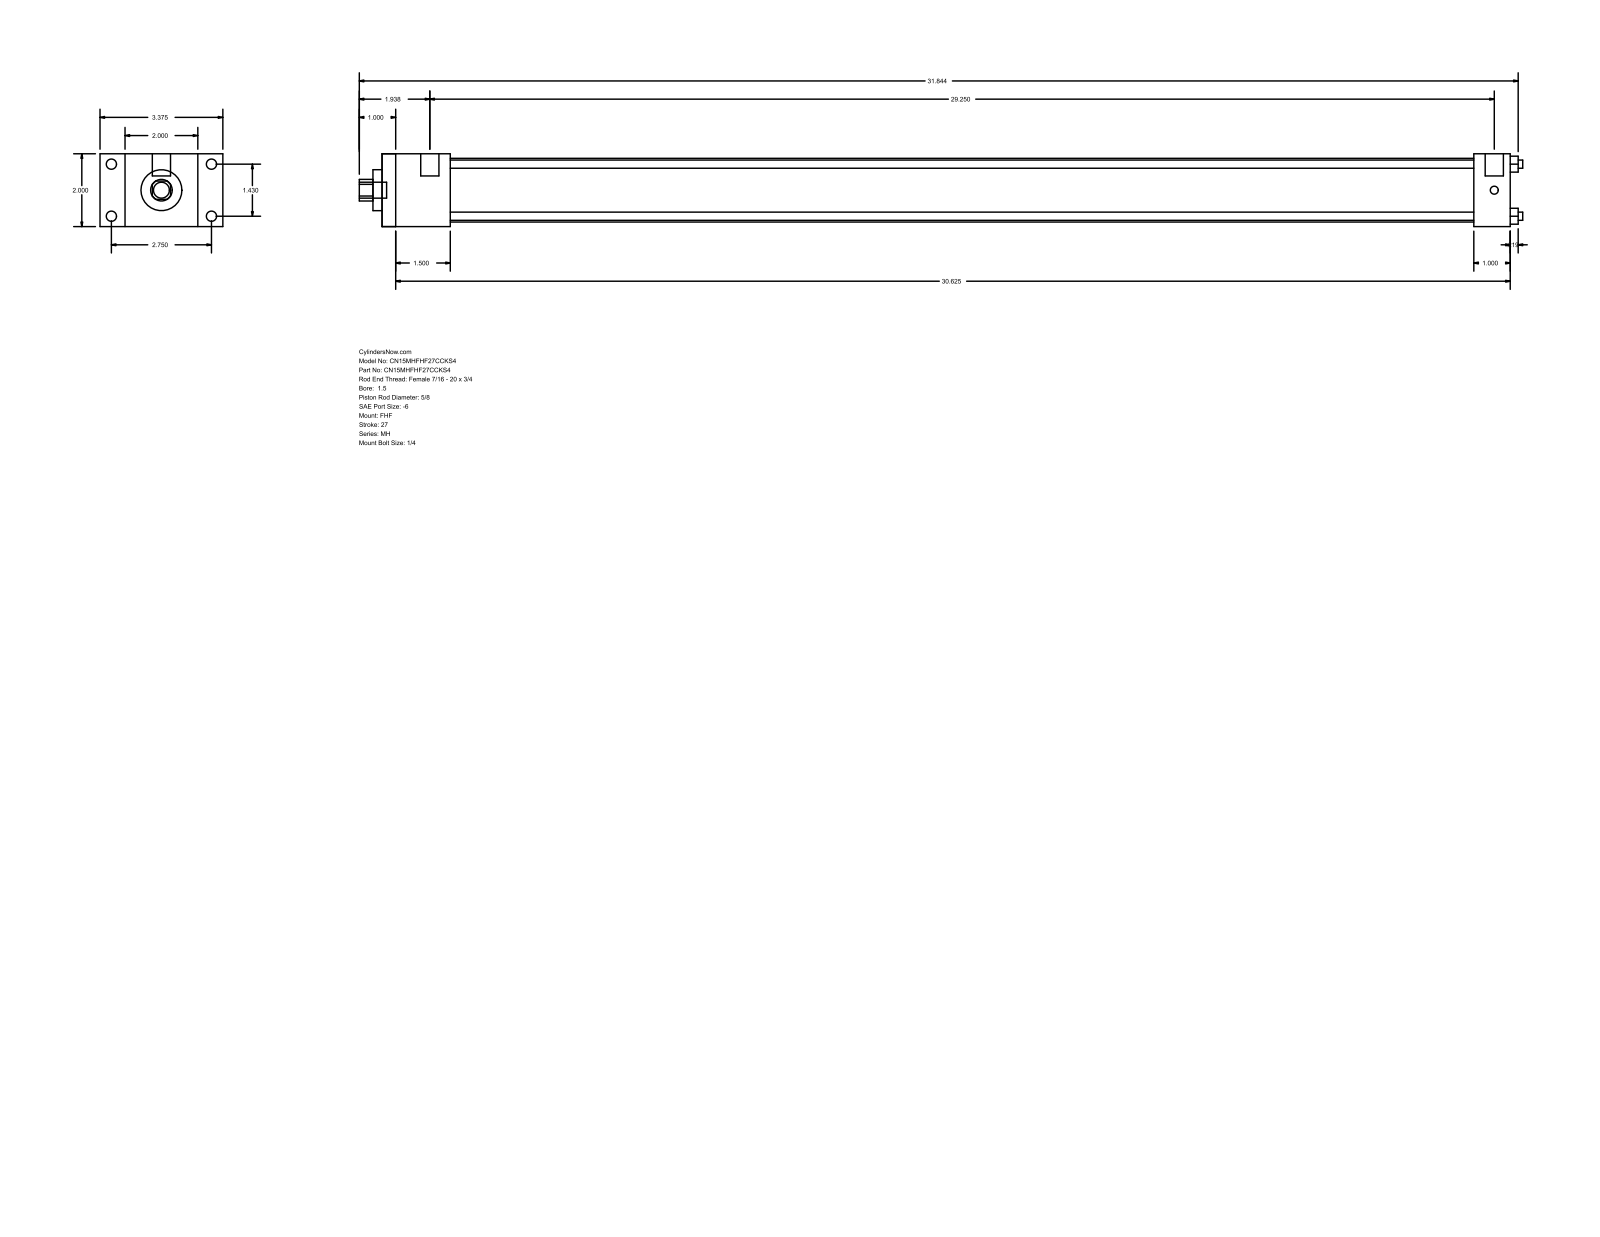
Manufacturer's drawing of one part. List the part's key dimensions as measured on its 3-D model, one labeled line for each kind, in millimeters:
Part name (STEP PRODUCT): MH_FHF__0150_0.625
STEP written by: GSSL Pune (CONFIG_CONTROL_DESIGN)
Units: millimetres
Bodies: 0 solids, 88 faces (60 planar, 28 cylindrical, 0 other)
Overall size (bounding box): 812.01 × 85.72 × 50.8
Round holes (diameter × count): ⌀5.71 ×4, ⌀15.88 ×1, ⌀28.57 ×1, ⌀44.45 ×1
Round bosses / shafts (diameter × count): ⌀7.14 ×4, ⌀5.56 ×4, ⌀12.7 ×2, ⌀11.11 ×1
Partial cylindrical surfaces — rounded edges, fillets, slot ends (radius × count): R7.54 ×1
Main face-to-face distances: 50.8, 17.46, 68.26, 47.62, 85.72, 787.39, 739.77, 762, 714.38, 25.39
Hole centre spacings: 25.68, 36.32, 51.36
